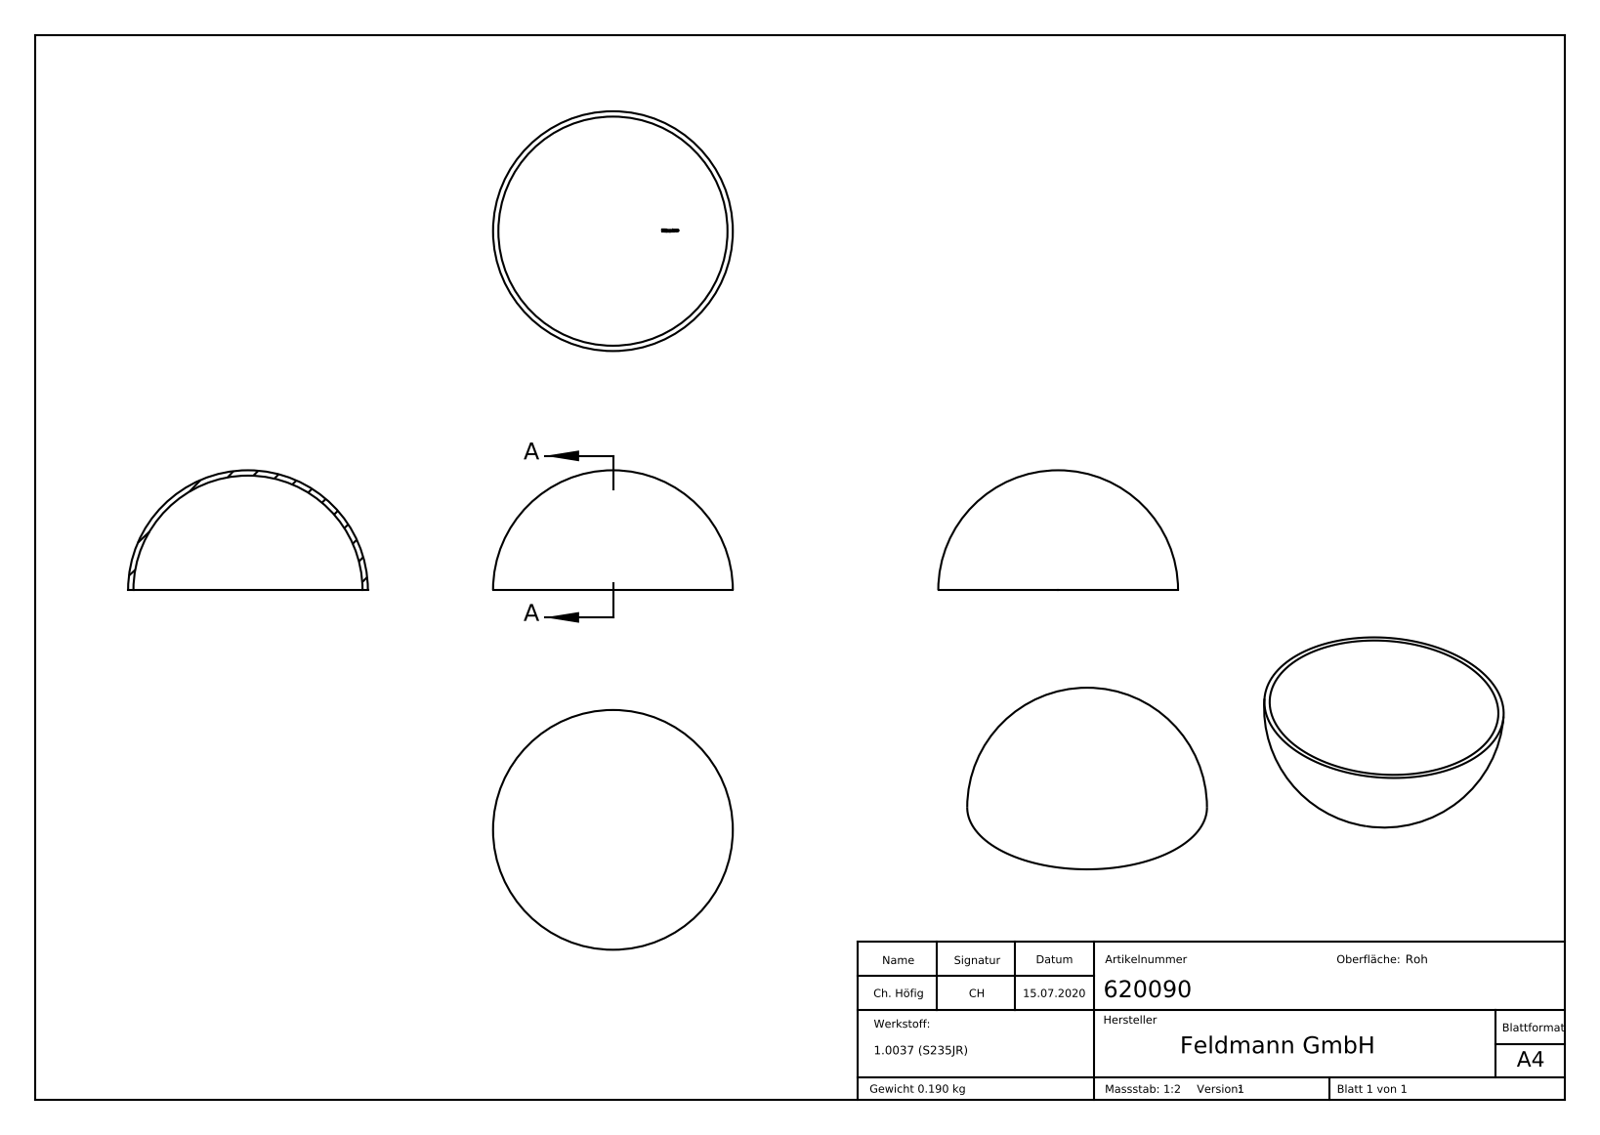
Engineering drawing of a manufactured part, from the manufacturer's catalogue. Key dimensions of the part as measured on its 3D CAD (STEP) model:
Part name (STEP PRODUCT): 620090
STEP written by: SolidWorks 2018 (CONFIG_CONTROL_DESIGN)
Units: millimetres
Bodies: 1 solid, 190 faces (67 planar, 0 cylindrical, 123 other)
Overall size (bounding box): 90 × 90 × 45
Volume: 24 333 mm³ · Surface area: 24 898 mm²
Main face-to-face distances: 1.19, 0.55, 0.5, 0.81, 0.45, 0.66, 1.74, 1.31, 0.53, 1.47
